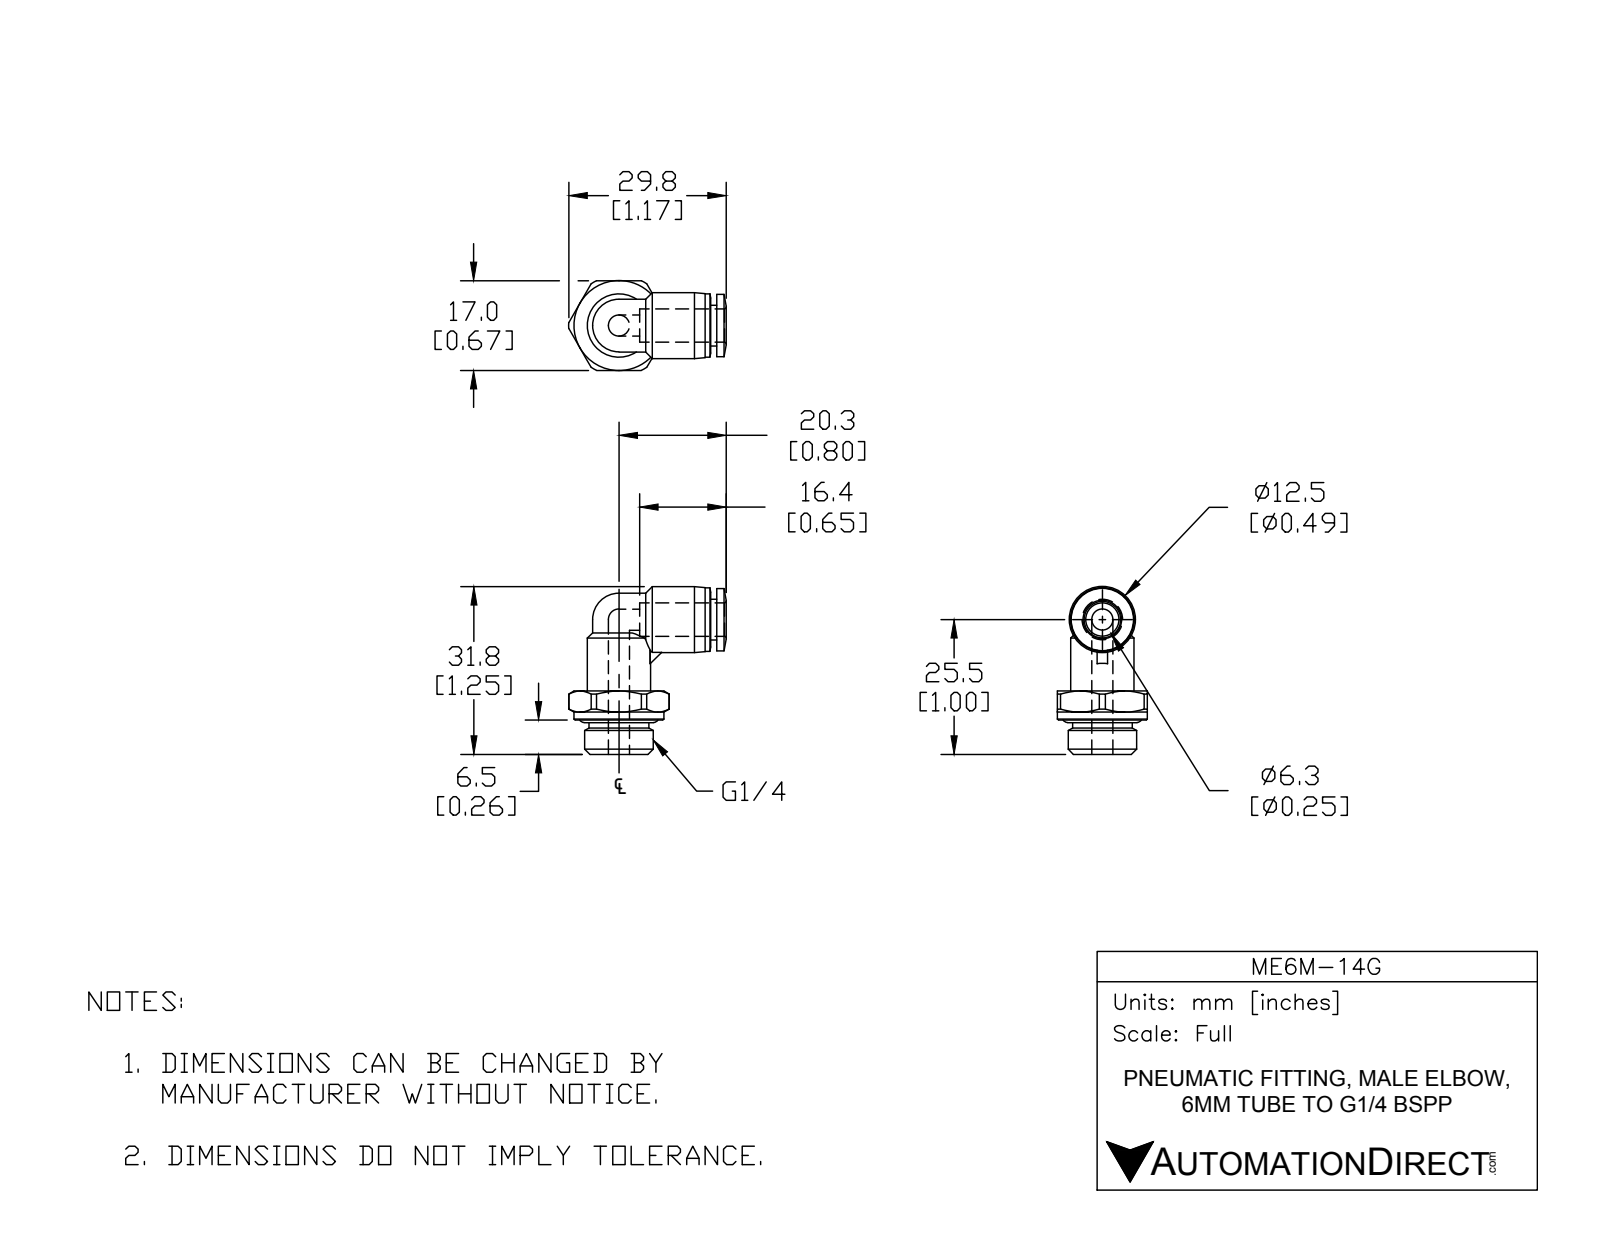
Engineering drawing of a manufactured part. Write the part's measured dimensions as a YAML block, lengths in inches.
part_name: "ME6M-14G"
step_written_by: "SolidWorks 2018 (AUTOMOTIVE_DESIGN)"
units: inches
bodies: {solids: 2, faces: 90, planar: 18, cylindrical: 31, other: 41}
overall_size: [1.25, 1.173, 0.669]
volume: 0.288
surface_area: 5.212
round_holes:
  - {diameter: 0.157, count: 2}
  - {diameter: 0.248, count: 1}
round_bosses_or_shafts:
  - {diameter: 0.472, count: 2}
  - {diameter: 0.669, count: 1}
  - {diameter: 0.51, count: 1}
  - {diameter: 0.492, count: 1}
  - {diameter: 0.465, count: 1}
  - {diameter: 0.445, count: 1}
  - {diameter: 0.303, count: 1}
partial_cylinders:
  - {radius: 0.197, count: 2}
  - {radius: 0.374, count: 1}
face_to_face_distances: [0.669, 0.472, 0.045, 0.311, 0.161, 0.53, 0.575, 0.256, 0.055, 0.217]
